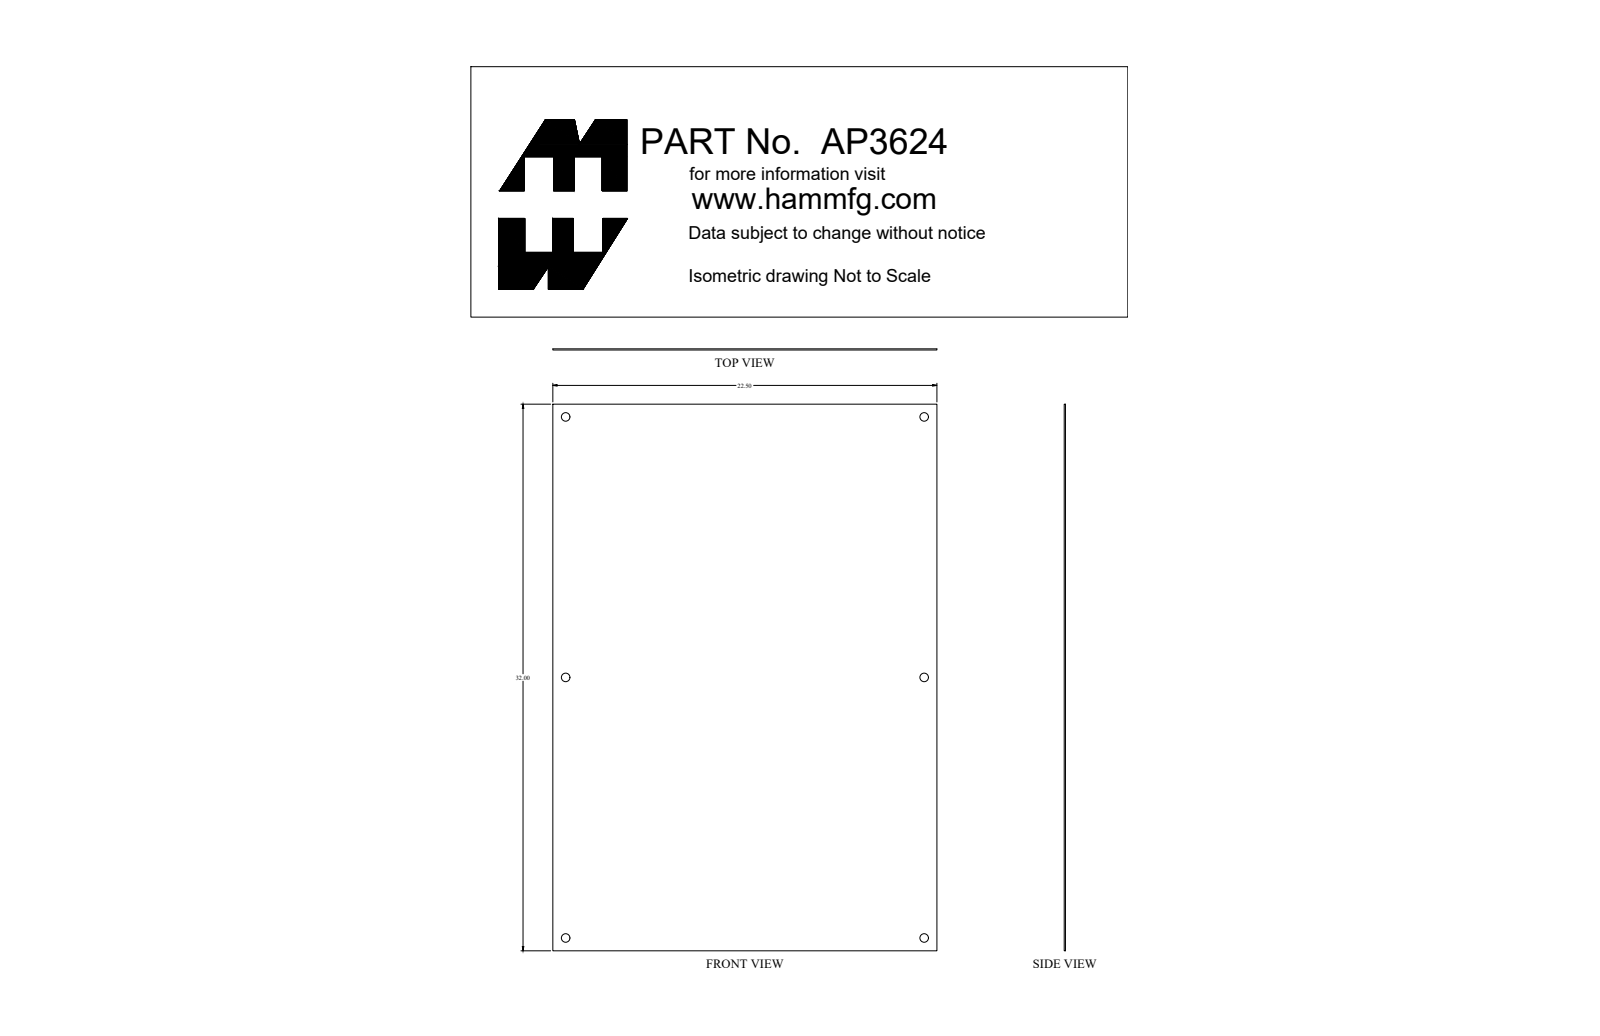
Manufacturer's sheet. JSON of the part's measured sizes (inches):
{"part_name": "AP3624_Default", "step_written_by": "SolidWorks 2019 (CONFIG_CONTROL_DESIGN)", "units": "inches", "bodies": {"solids": 1, "faces": 18, "planar": 6, "cylindrical": 12, "other": 0}, "overall_size": [32, 22.5, 0.072], "volume_in3": 51.76, "surface_area_in2": 1446, "round_holes": [[0.5, 6]], "face_to_face_distances": [0.072, 22.5, 32], "hole_center_spacings": [15.25, 25.953, 21, 30.5, 37.03]}
